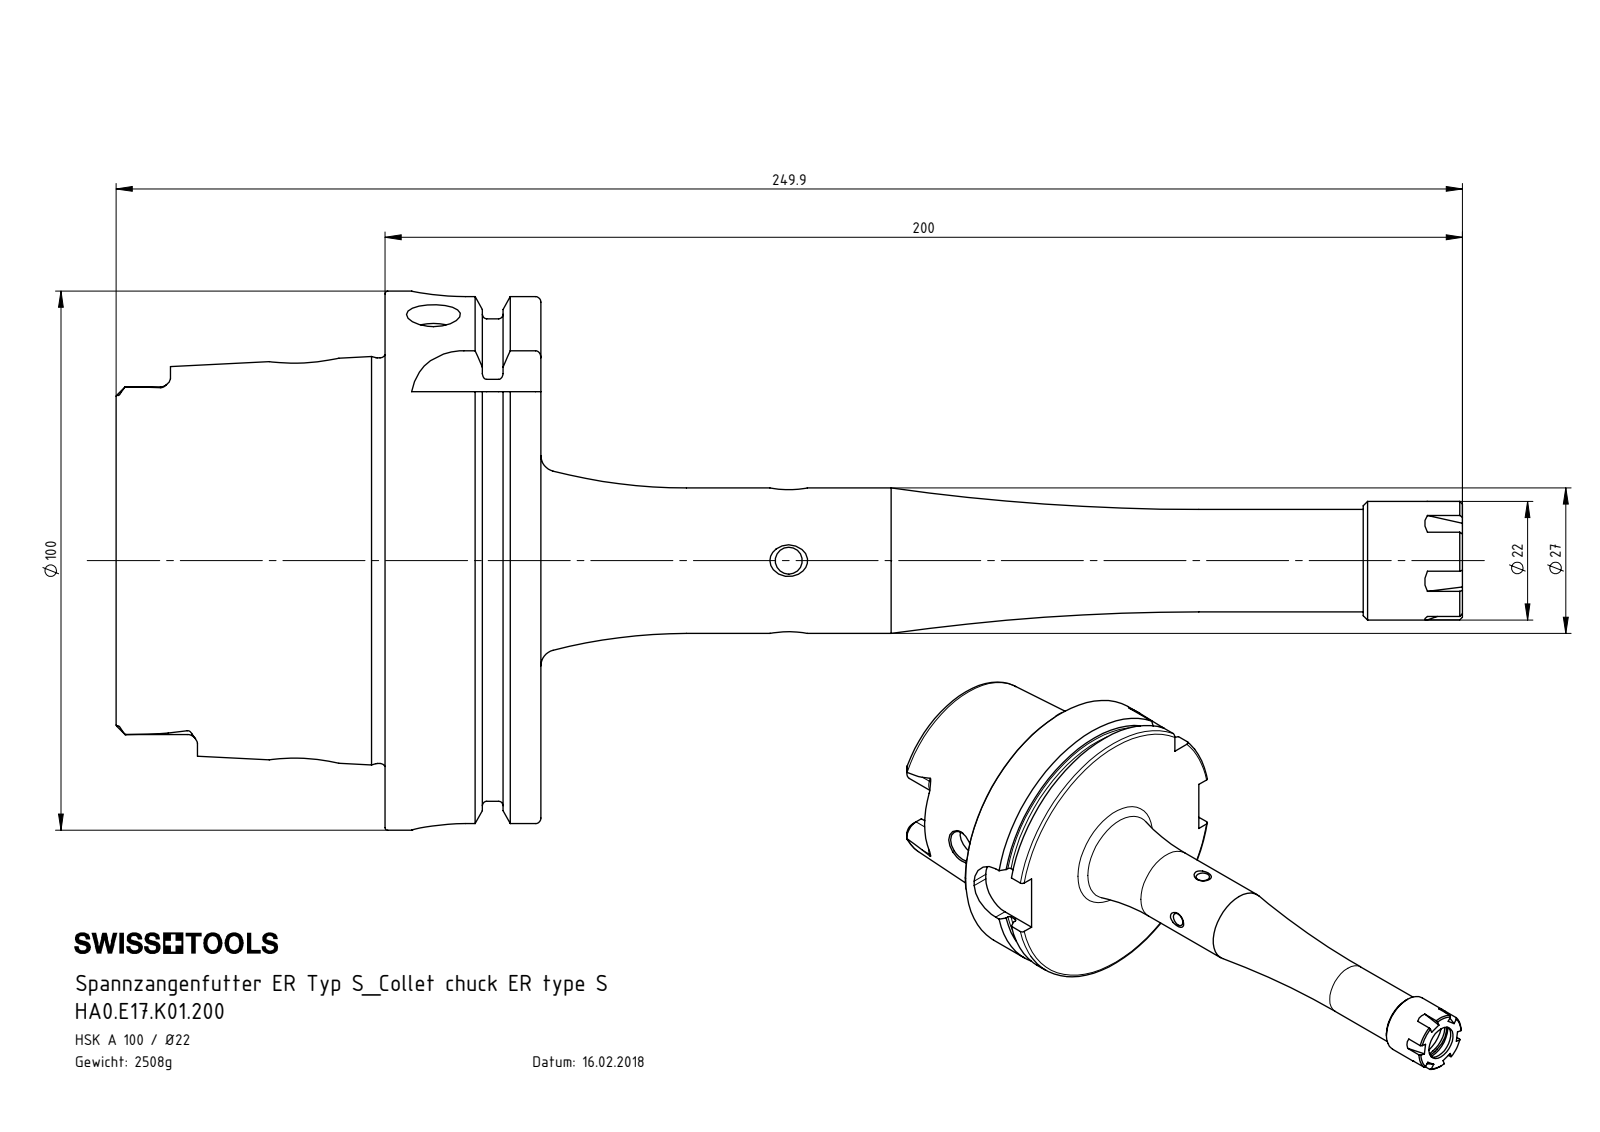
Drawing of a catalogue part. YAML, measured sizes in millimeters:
part_name: "HA0-E17.K01.200_C_Fertigbearbeitung; E17-ER1.001.018; ERU-AN2.K01.016_A; HA0.E17.K01.200"
step_written_by: "SolidWorks 2017 (CONFIG_CONTROL_DESIGN)"
units: millimeters
bodies: {solids: 3, faces: 297, planar: 99, cylindrical: 81, other: 117}
overall_size: [249.9, 100, 100]
volume: 319441
surface_area: 68348
round_holes:
  - {diameter: 5, count: 3}
  - {diameter: 10, count: 3}
  - {diameter: 3, count: 1}
  - {diameter: 6.8, count: 1}
  - {diameter: 10.5, count: 1}
  - {diameter: 12, count: 1}
  - {diameter: 12.7, count: 1}
  - {diameter: 18, count: 1}
  - {diameter: 20, count: 1}
  - {diameter: 22.5, count: 1}
  - {diameter: 26, count: 1}
  - {diameter: 53, count: 1}
round_bosses_or_shafts:
  - {diameter: 100, count: 1}
  - {diameter: 91.95, count: 1}
  - {diameter: 75.26, count: 1}
  - {diameter: 27, count: 1}
  - {diameter: 22, count: 1}
  - {diameter: 19, count: 1}
  - {diameter: 6, count: 1}
partial_cylinders:
  - {radius: 1.9, count: 6}
  - {radius: 4.88, count: 4}
  - {radius: 10, count: 4}
  - {radius: 7.7, count: 2}
face_to_face_distances: [28.95, 12.45, 16.5, 49.9, 62.35, 78.85, 78.2, 28.3, 15.85, 0.65]
hole_center_spacings: [67.95, 89.95]
